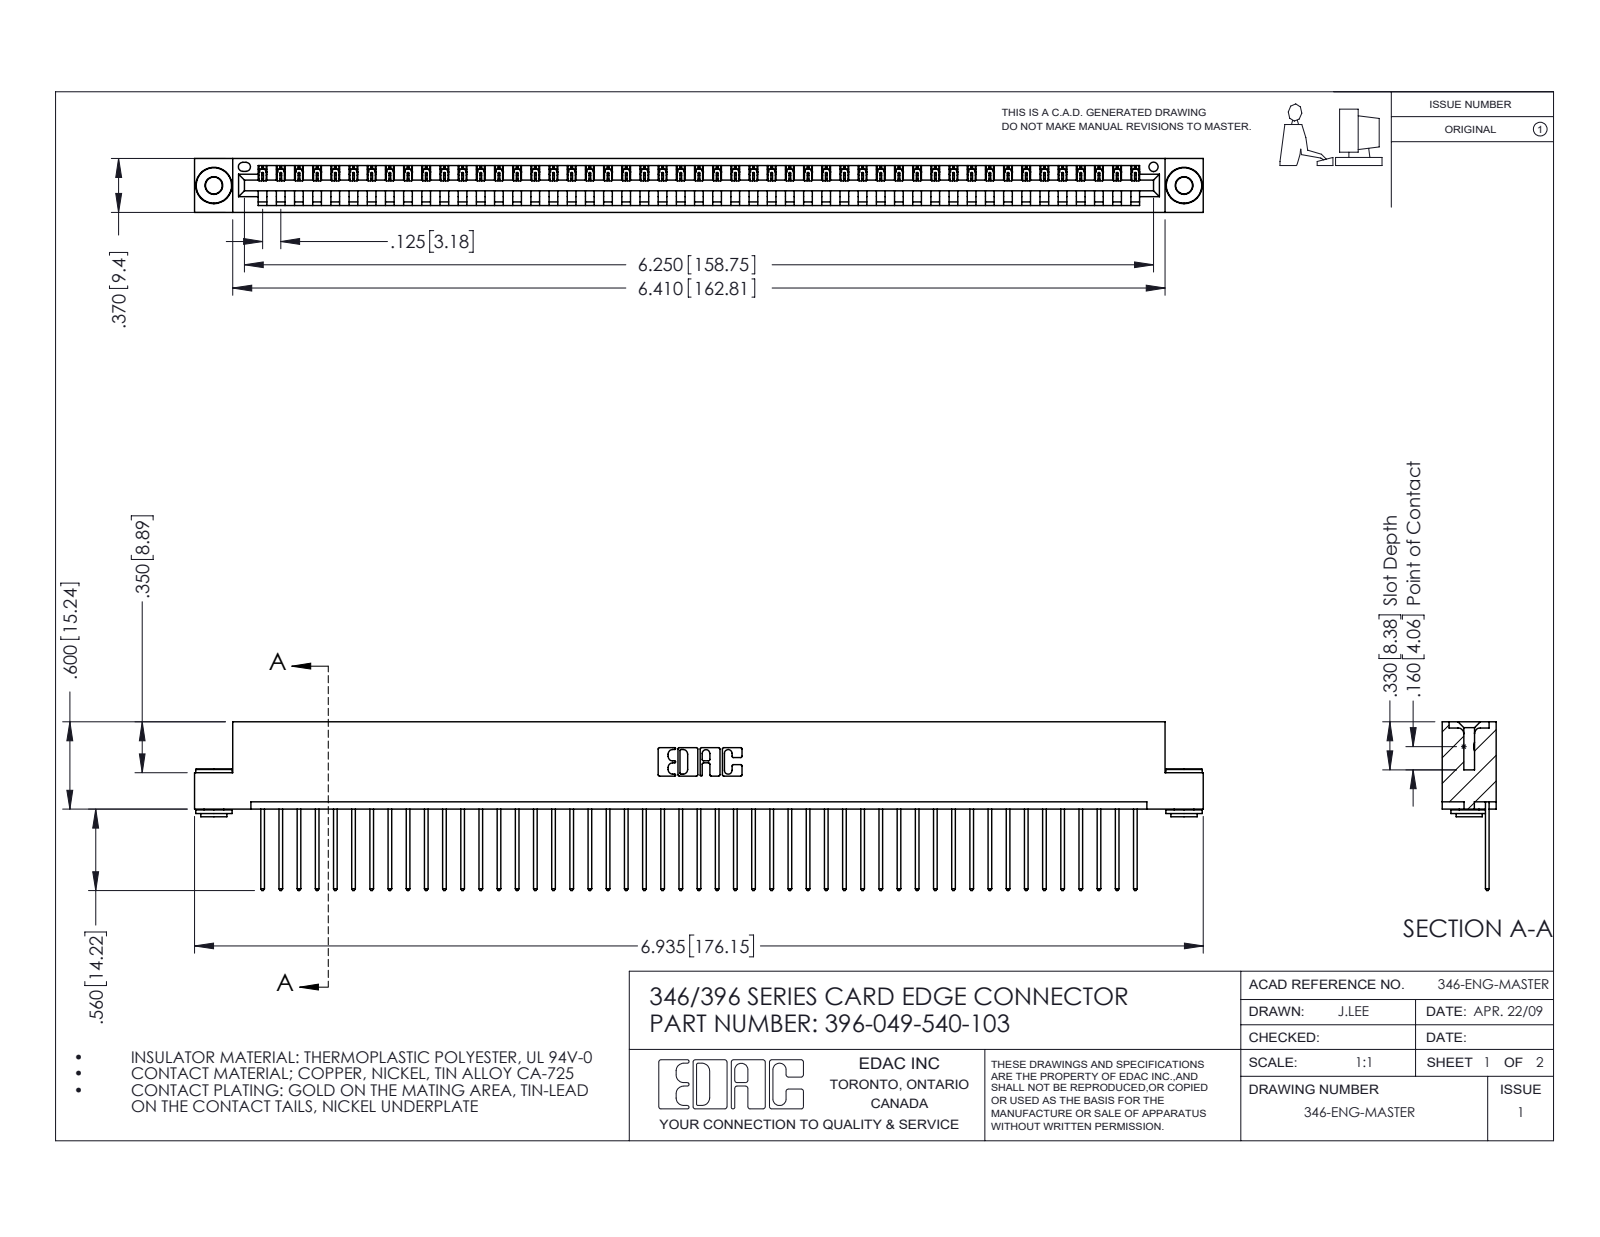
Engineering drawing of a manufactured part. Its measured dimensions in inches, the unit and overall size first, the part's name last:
Units: inches
Overall size (bounding box): 6.935 × 1.16 × 0.37
Round holes (diameter × count): ⌀0.116 ×2, ⌀0.156 ×2, ⌀0.064 ×1
Round bosses / shafts (diameter × count): ⌀0.25 ×2, ⌀0.18 ×2, ⌀0.136 ×2
Partial cylindrical surfaces — rounded edges, fillets, slot ends (radius × count): R0.006 ×98, R0.01 ×98, R0.01 ×22, R0.007 ×6, R0.031 ×6, R0.026 ×3, R0.031 ×2, R0.04 ×2
Main face-to-face distances: 0.048, 0.322, 0.37, 0.25, 0.025, 0.072, 0.298, 0.148, 0.222, 0.1
Hole centre spacings: 0.246, 6.461, 6.67
Volume: 1.037 in³ · Surface area: 34.13 in²
Bodies: 52 solids, 3002 faces (2046 planar, 948 cylindrical, 8 other)
Part name (STEP PRODUCT): 345-250-002_345-250-002-102; 345-292-001_345-293-140; 346 Part_Flush Mounting Lugs - 0.156 Dia-TH; 396-049-540-103
STEP written by: SolidWorks 2016 (CONFIG_CONTROL_DESIGN)
